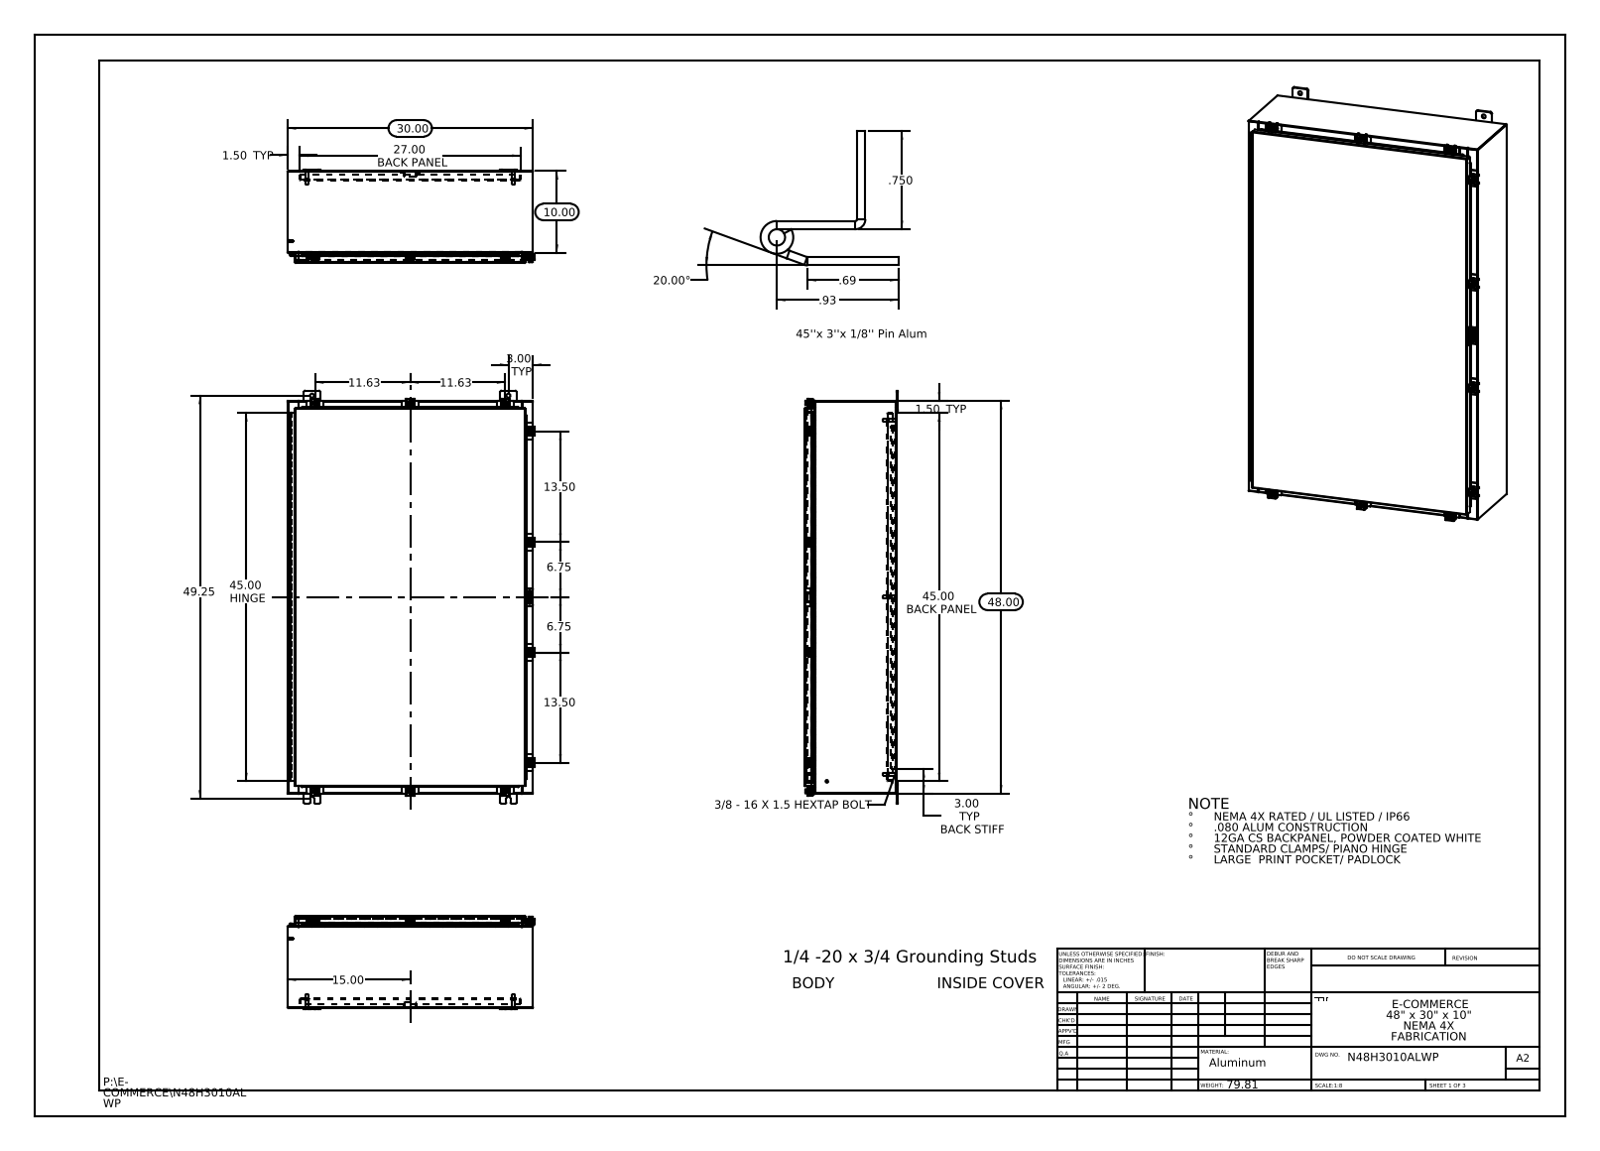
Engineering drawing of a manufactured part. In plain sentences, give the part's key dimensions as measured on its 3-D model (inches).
The part is named "N48H3010ALWP Standard Clamps; N48H3010ALWP Hinge Cover Side; N48H3010ALWP Padlock Staple; N48H3010ALWP Clamp Assembly (+8 more)". Its 3-D file was written by "SolidWorks 2013 (CONFIG_CONTROL_DESIGN)". It is 72 solids with 2887 faces: 1498 planar, 1229 cylindrical and 160 other. Overall it measures 50.5 by 30.211 by 11.389 inches. Its volume is 518.7 cubic inches and its surface area 12 923 square inches. Round holes: 10 of diameter 0.213, 10 of diameter 0.26, 10 of diameter 0.5, 2 of diameter 0.125, 1 of diameter 0.125. Round bosses or shafts: 11 of diameter 0.25, 10 of diameter 0.5, 10 of diameter 0.399, 6 of diameter 0.625, 6 of diameter 0.375, 6 of diameter 0.33, 2 of diameter 0.315, 2 of diameter 0.236. Partial cylindrical surfaces (rounded edges, fillets, slot ends): 46 of radius 0.06, 31 of radius 0.013, 25 of radius 0.088, 24 of radius 0.19, 20 of radius 0.12, 20 of radius 0.141, 15 of radius 0.05, 14 of radius 0.08. The main face-to-face distances are 0.075, 11.126, 11.051, 0.104, 11.201, 1, 10.126, 1.075, 10.051, 1.179. The hole center spacings are 21.625, 26.876, 33.245, 45.362, 47.075, 48.854, 13.5, 25.25.
